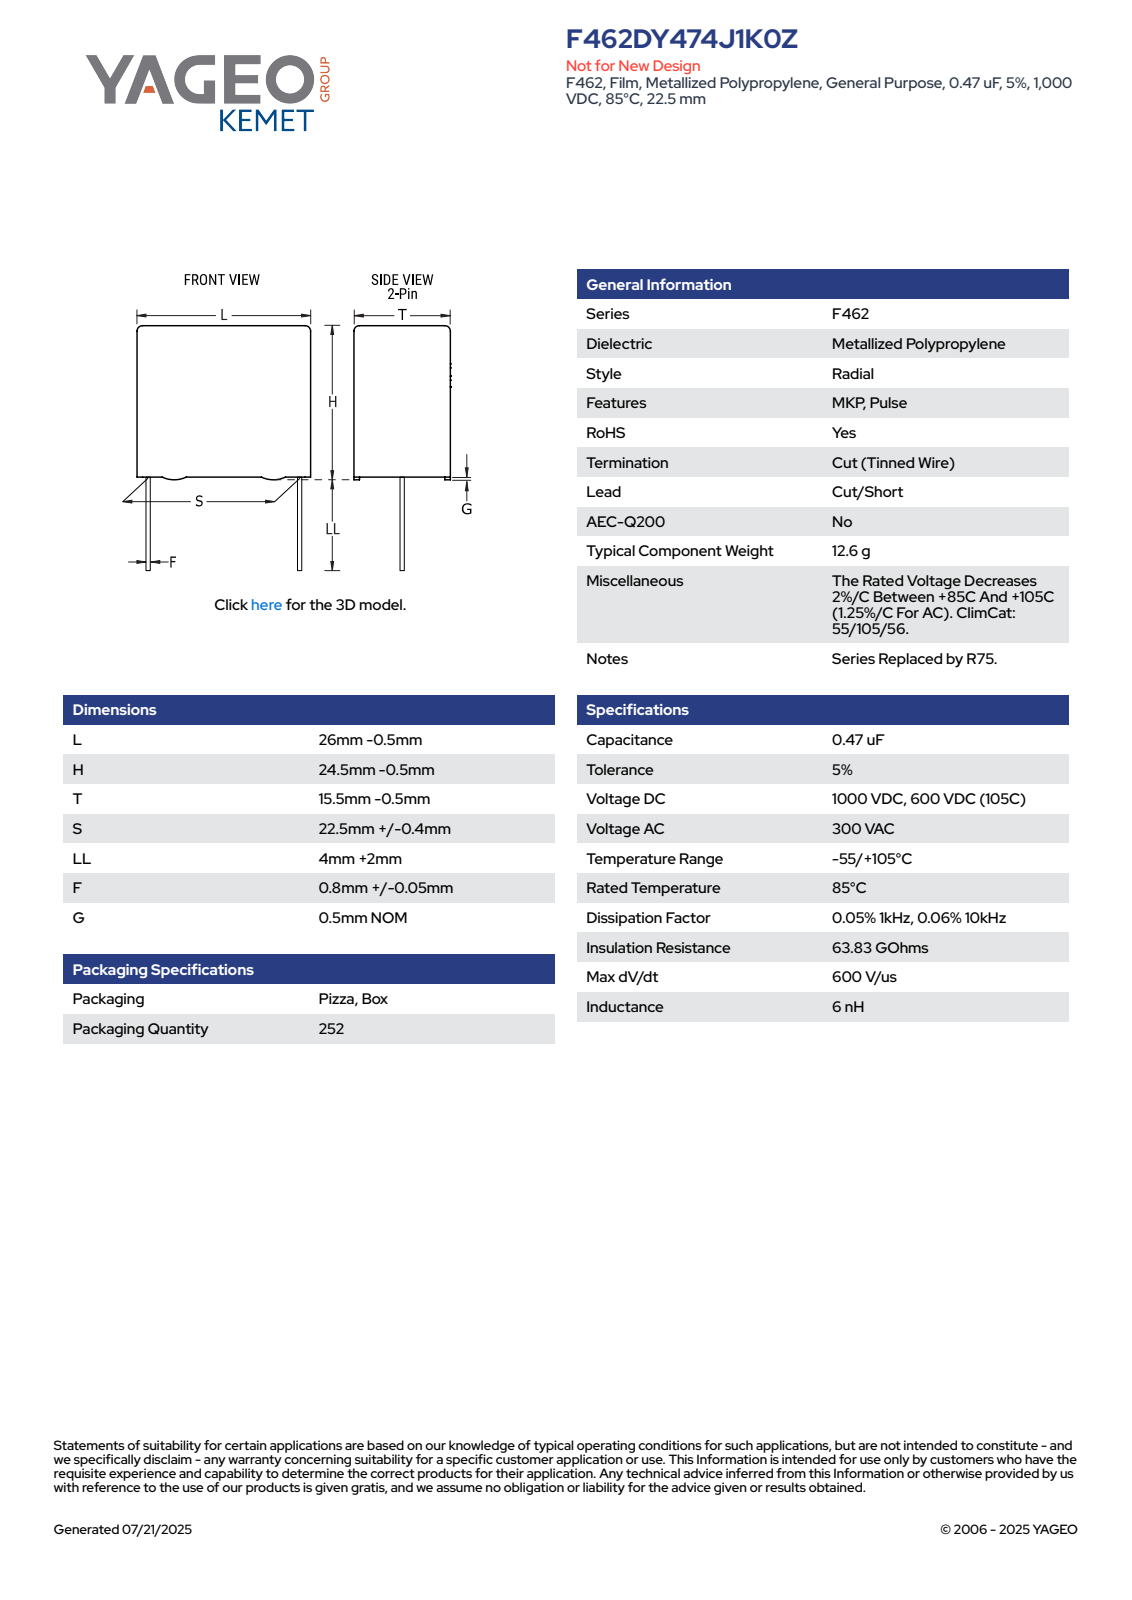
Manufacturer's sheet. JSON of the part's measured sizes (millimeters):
{"part_name": "CFR_RBG_26X24.5X15.5_L25.5H24T15S22.5LL6F0.85G0.5", "step_written_by": "SolidWorks 2014 (AUTOMOTIVE_DESIGN)", "units": "millimeters", "bodies": {"solids": 4, "faces": 89, "planar": 81, "cylindrical": 8, "other": 0}, "overall_size": [30, 25.5, 15.01], "volume_mm3": 8999, "surface_area_mm2": 2775, "round_bosses_or_shafts": [[0.85, 2]], "partial_cylinders_radius": [[0.5, 4]], "face_to_face_distances": [15, 25.5, 23.5, 0.5, 24, 0.85, 14.14, 0.86, 13.29, 14.15]}
